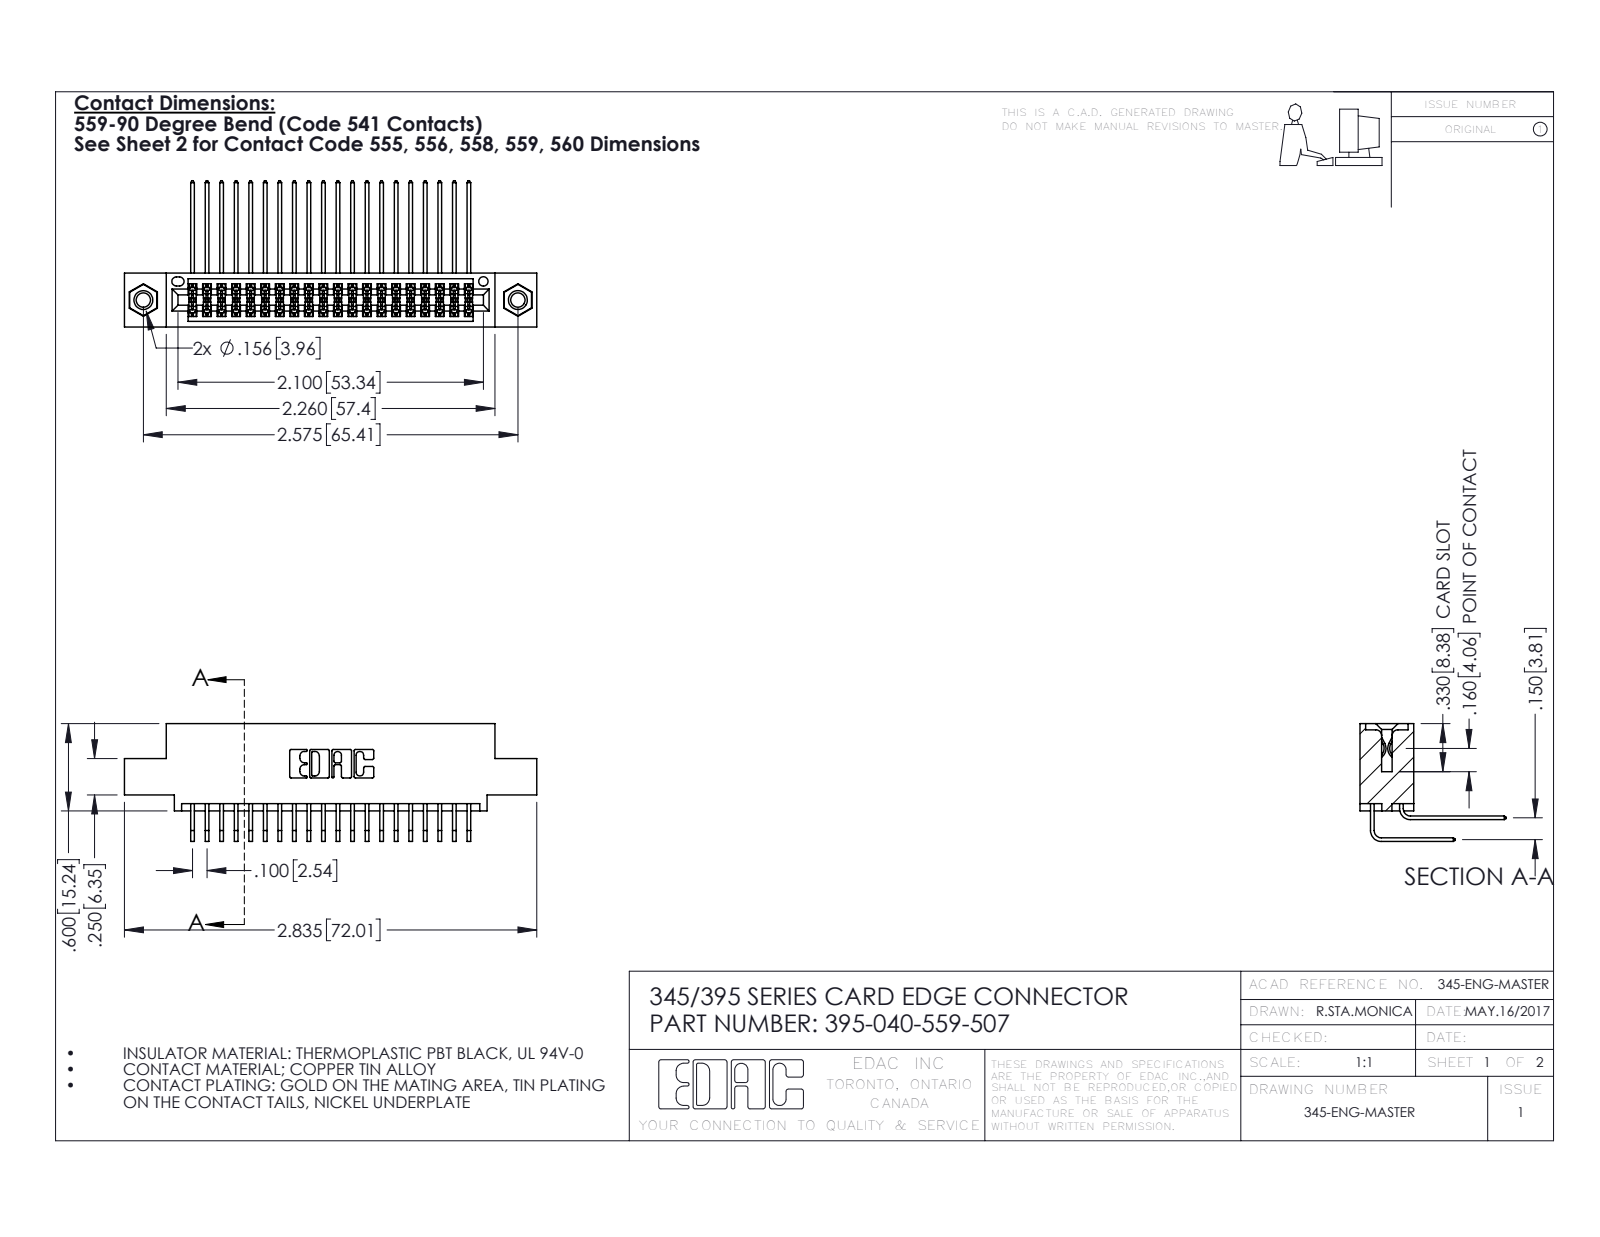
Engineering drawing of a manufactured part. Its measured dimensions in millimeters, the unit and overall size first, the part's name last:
Units: millimetres
Overall size (bounding box): 72 × 25.5 × 20.5
Round holes (diameter × count): ⌀2.5 ×2, ⌀3.2 ×2, ⌀4 ×2, ⌀1.6 ×1
Round bosses / shafts (diameter × count): ⌀3.9 ×2
Partial cylindrical surfaces — rounded edges, fillets, slot ends (radius × count): R0.2 ×60, R0.3 ×22, R0.2 ×6, R0.8 ×6, R0.7 ×3, R0.4 ×2, R0.5 ×2, R0.6 ×2
Main face-to-face distances: 1.8, 7.6, 5.1, 9.4, 2.5, 6.9, 0.6, 5.7, 3.8, 4.4
Hole centre spacings: 6.9, 59.5, 65.4
Volume: 6 930 mm³ · Surface area: 11 030 mm²
Bodies: 43 solids, 2270 faces (1516 planar, 738 cylindrical, 16 other)
Part name (STEP PRODUCT): 395-040-559-507; 345-250-001_345-250-005-103; 345 Part_0.110 Offset - 0.156 Dia-TI; 345-292-001_558 559 Tail - 1 (+1 more)
STEP written by: SolidWorks 2016 (CONFIG_CONTROL_DESIGN)
